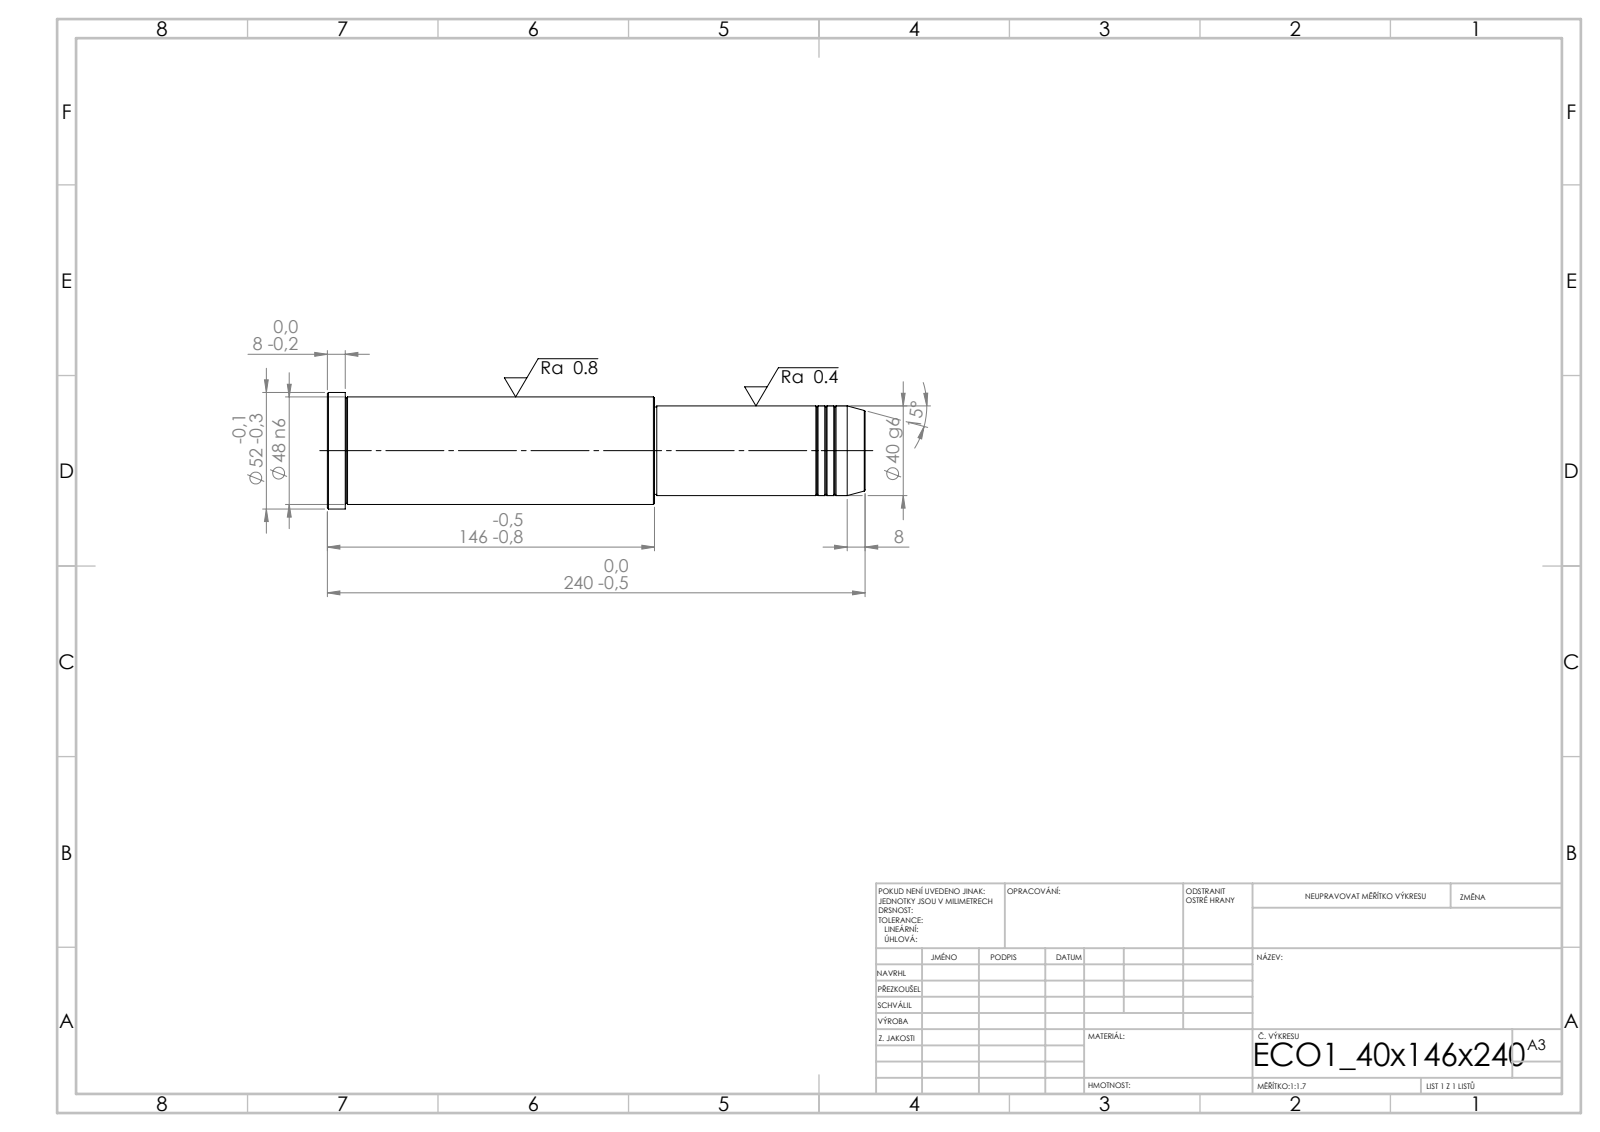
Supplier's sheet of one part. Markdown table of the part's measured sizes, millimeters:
| quantity | value |
| --- | --- |
| STEP written by | SolidWorks 2019 (CONFIG_CONTROL_DESIGN) |
| units | millimeters |
| bodies | 1 solid, 43 faces (5 planar, 14 cylindrical, 24 other) |
| overall size | 240 × 52 × 52 |
| volume | 383 484 mm³ |
| surface area | 38 206 mm² |
| round bosses / shafts (diameter × count) | 52 × 1, 48 × 1, 40 × 1, 39 × 1 |
| main face-to-face distances | 240, 94, 146, 232, 138, 8, 93, 1, 139, 147 |
